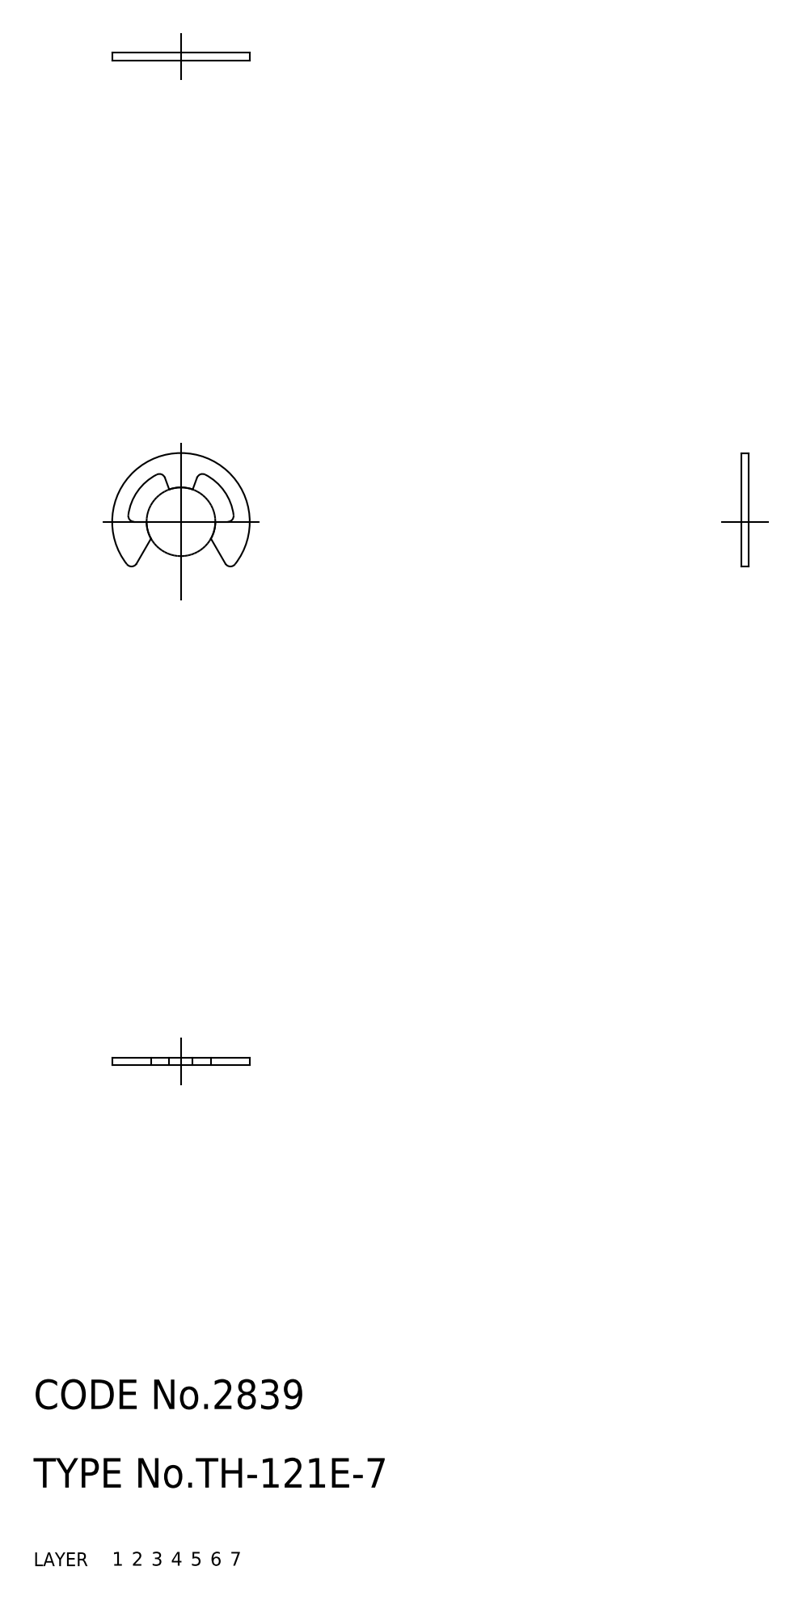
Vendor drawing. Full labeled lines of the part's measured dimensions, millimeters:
Part name (STEP PRODUCT): retainer
STEP written by: CADfix (AUTOMOTIVE_DESIGN)
Units: millimetres
Bodies: 1 solid, 20 faces (0 planar, 0 cylindrical, 20 other)
Overall size (bounding box): 14 × 11.55 × 0.8
Volume: 50 mm³ · Surface area: 178 mm²
